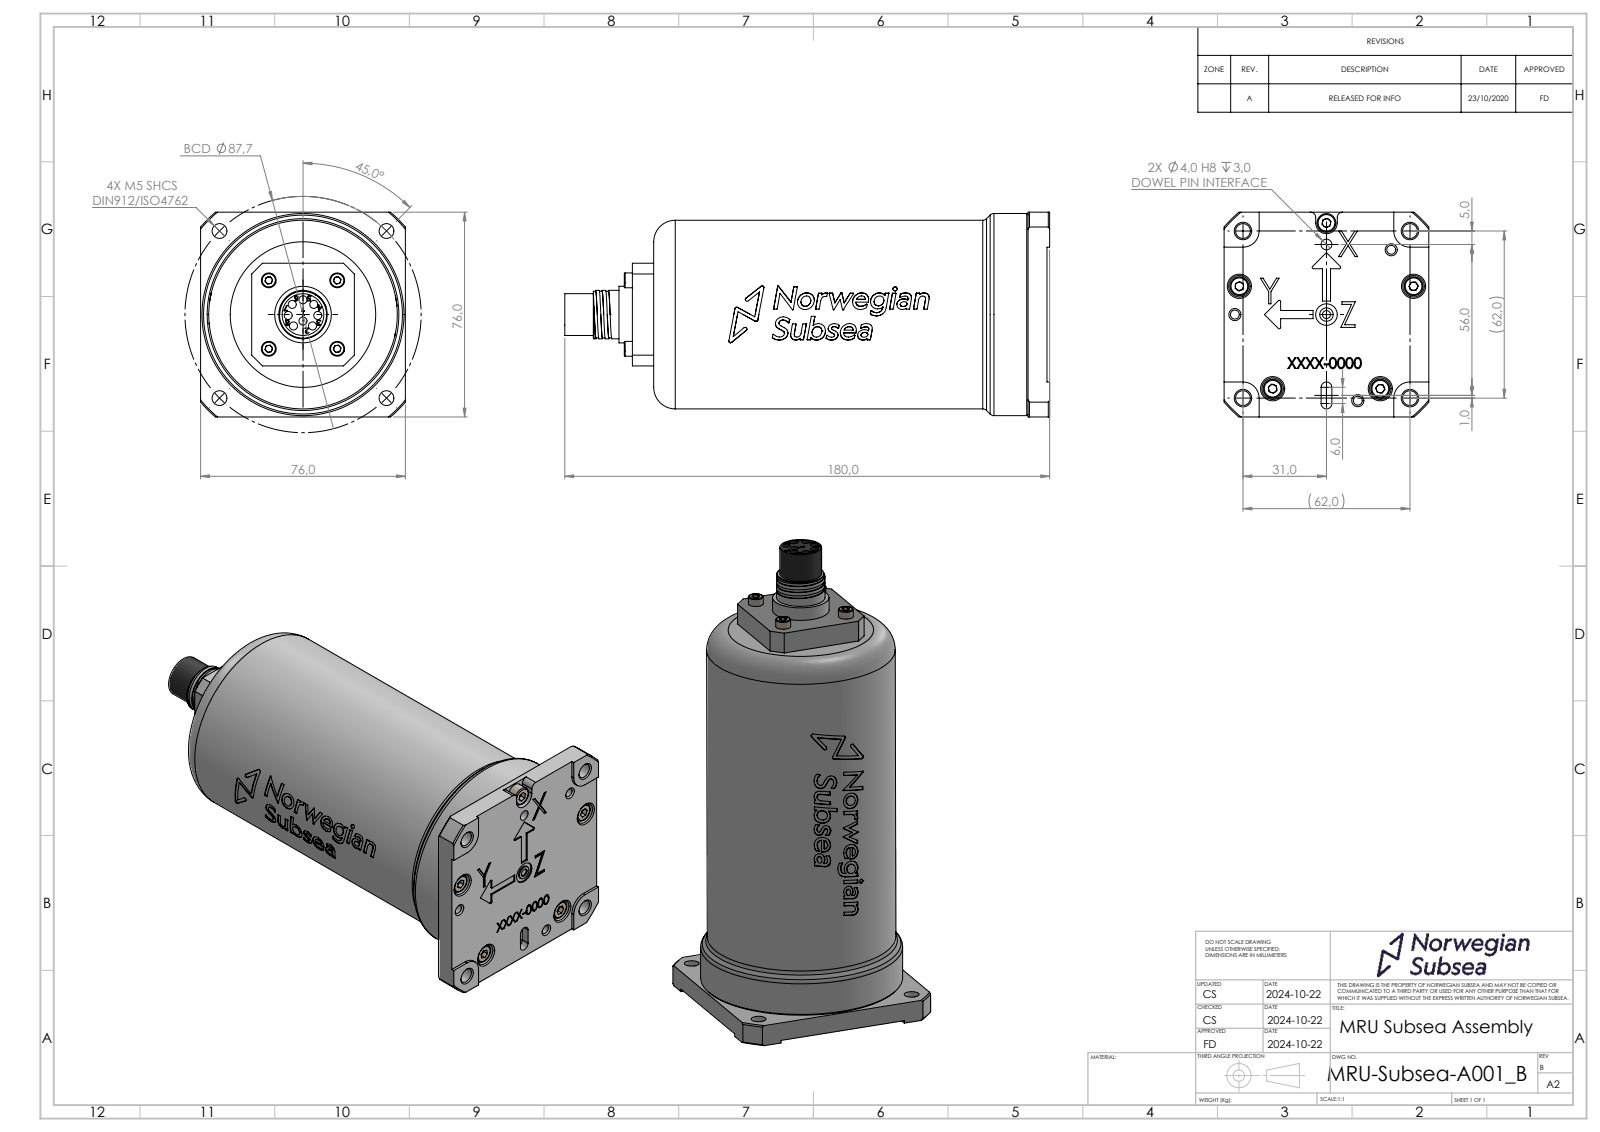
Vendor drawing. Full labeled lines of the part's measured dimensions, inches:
Part name (STEP PRODUCT): FCR1508F; O-ring; socket head cap screw_din_DIN 912 M4 x 10 --- 10N; O-ring_conn1 (+6 more)
STEP written by: SolidWorks 2024 (AUTOMOTIVE_DESIGN)
Units: inches
Bodies: 18 solids, 1703 faces (460 planar, 312 cylindrical, 931 other)
Overall size (bounding box): 7.087 × 2.992 × 2.992
Volume: 16.65 in³ · Surface area: 153.9 in²
Round holes (diameter × count): ⌀0.13 ×11, ⌀0.118 ×9, ⌀0.177 ×5, ⌀0.315 ×5, ⌀0.165 ×4, ⌀0.205 ×4, ⌀0.217 ×4, ⌀0.063 ×3, ⌀0.276 ×3, ⌀0.157 ×1, ⌀0.547 ×1, ⌀1.043 ×1
Round bosses / shafts (diameter × count): ⌀0.059 ×8, ⌀0.276 ×5, ⌀0.157 ×5, ⌀0.217 ×4, ⌀0.118 ×4, ⌀2.953 ×1, ⌀2.756 ×1, ⌀2.402 ×1
Partial cylindrical surfaces — rounded edges, fillets, slot ends (radius × count): R0.015 ×5, R0.02 ×4, R0.079 ×4, R0.236 ×4, R0.008 ×2, R0.019 ×2, R0.031 ×2, R0.026 ×1
Main face-to-face distances: 0.276, 5.748, 0.512, 5.472, 4.961, 0.906, 4.843, 0.63, 5.236, 4.331
Hole centre spacings: 1.339, 1.865, 0.217, 0.315, 0.707, 0.778, 0.976, 1
